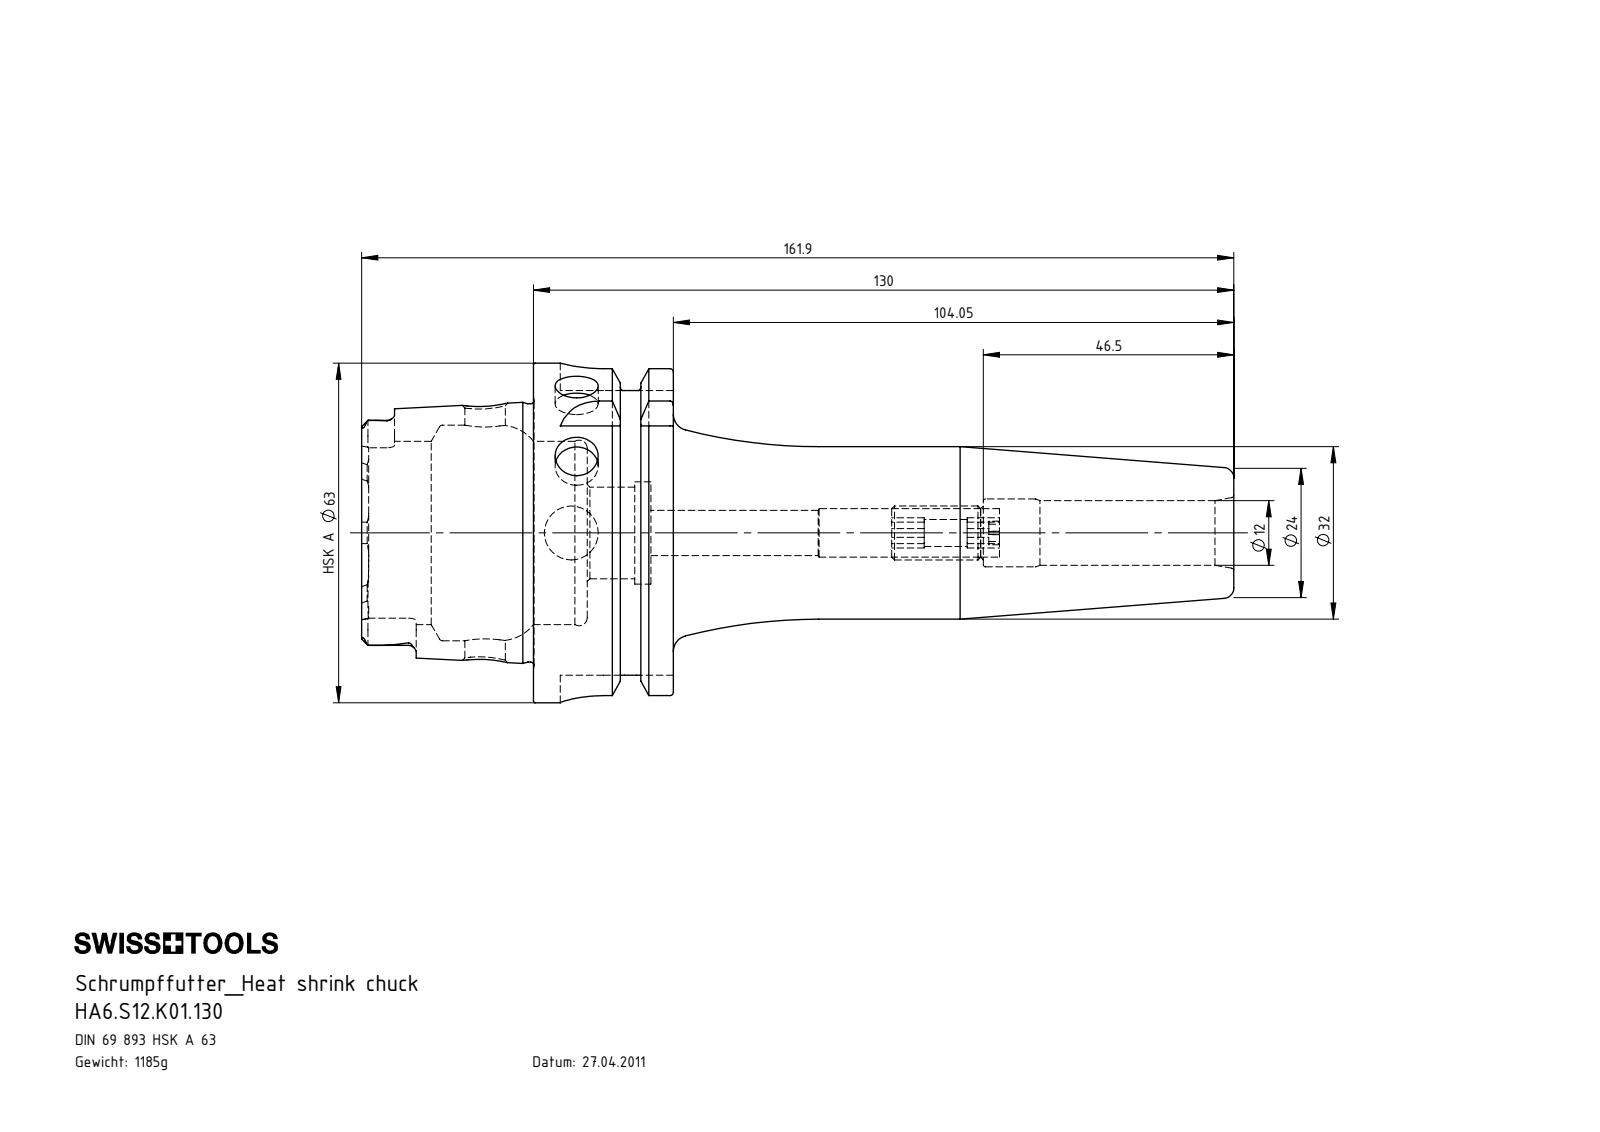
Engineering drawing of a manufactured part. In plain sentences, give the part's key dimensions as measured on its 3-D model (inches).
The part is named "HA6-S12.K01.130; ERU-AN4.K01.020_A; HA6-S12.K01.130_A_Fertigbearbeitung". Its 3-D file was written by "SolidWorks 2012 (AUTOMOTIVE_DESIGN)". It is 2 solids with 238 faces: 82 planar, 61 cylindrical and 95 other. Overall it measures 6.374 by 2.48 by 2.48 inches. Its volume is 9.215 cubic inches and its surface area 55.74 square inches. Round holes: 2 of diameter 0.315, 1 of diameter 0.197, 1 of diameter 0.295, 1 of diameter 0.331, 1 of diameter 0.354, 1 of diameter 0.394, 1 of diameter 0.472, 1 of diameter 0.496, 1 of diameter 0.669, 1 of diameter 0.748, 1 of diameter 1.339, 1 of diameter 1.575. Round bosses or shafts: 1 of diameter 2.48, 1 of diameter 2.163, 1 of diameter 1.887, 1 of diameter 1.26, 1 of diameter 0.394. Partial cylindrical surfaces (rounded edges, fillets, slot ends): 6 of radius 0.055, 4 of radius 0.113, 4 of radius 0.315. The main face-to-face distances are 1.022, 0.63, 0.392, 1.256, 1.648, 2.278, 2.079, 0.858, 0.467, 2.114.
